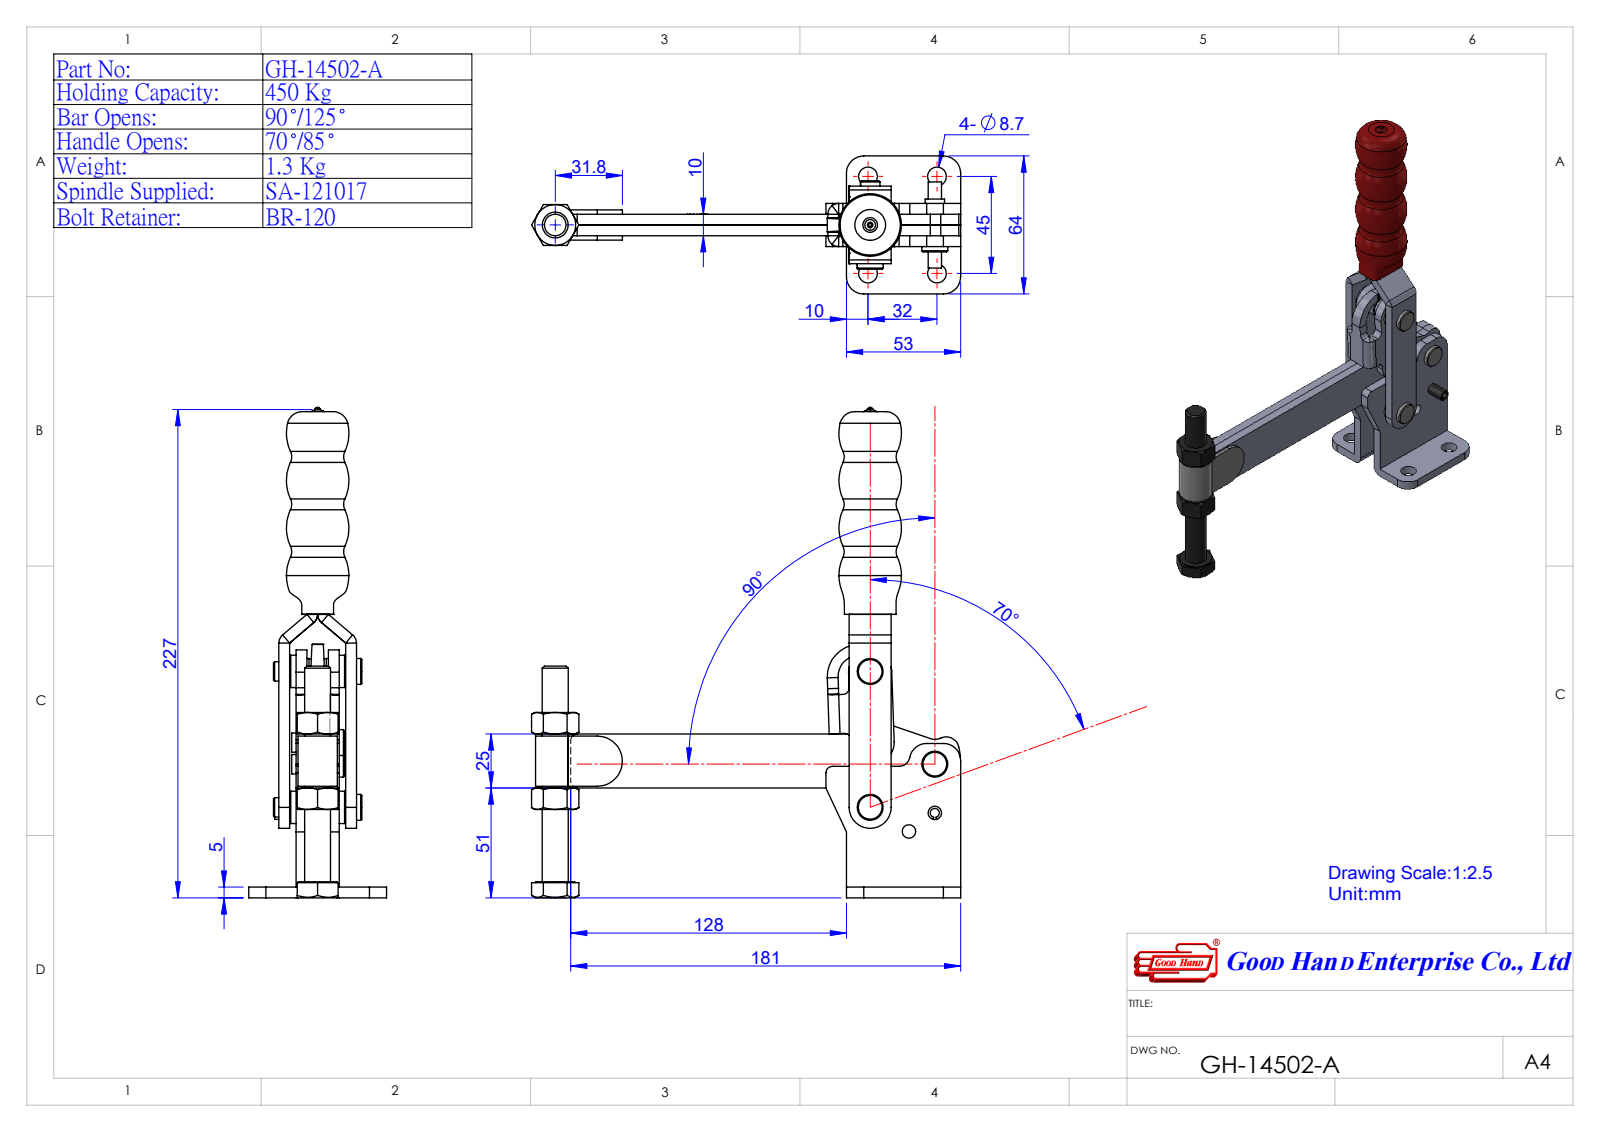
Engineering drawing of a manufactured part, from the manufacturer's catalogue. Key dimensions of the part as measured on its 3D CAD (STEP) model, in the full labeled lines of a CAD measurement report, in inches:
Part name (STEP PRODUCT): Group6^GH-14502-A(簡化)-1; GH-14502-A(簡化)-1; Group3^GH-14502-A(簡化)-1; Group5^GH-14502-A(簡化)-1 (+3 more)
STEP written by: SolidWorks 2016 (AUTOMOTIVE_DESIGN)
Units: inches
Bodies: 6 solids, 618 faces (272 planar, 153 cylindrical, 193 other)
Overall size (bounding box): 8.957 × 8.934 × 2.52
Volume: 12.58 in³ · Surface area: 117.6 in²
Round holes (diameter × count): ⌀0.276 ×4, ⌀0.343 ×4, ⌀0.075 ×1, ⌀0.236 ×1, ⌀0.402 ×1, ⌀0.472 ×1
Round bosses / shafts (diameter × count): ⌀0.394 ×4, ⌀0.512 ×2, ⌀0.354 ×2, ⌀0.352 ×2, ⌀0.709 ×1, ⌀0.244 ×1, ⌀0.072 ×1
Partial cylindrical surfaces — rounded edges, fillets, slot ends (radius × count): R0.197 ×6, R0.315 ×5, R0.029 ×3, R0.03 ×3, R0.118 ×2, R0.119 ×2, R0.236 ×2, R0.394 ×2
Main face-to-face distances: 0.197, 0.394, 0.591, 0.315, 0.906, 0.787, 0.512, 0.118, 0.709, 1.102
Hole centre spacings: 1.26, 1.772, 2.174, 6.898, 8.15, 0.835, 1.183, 1.202
